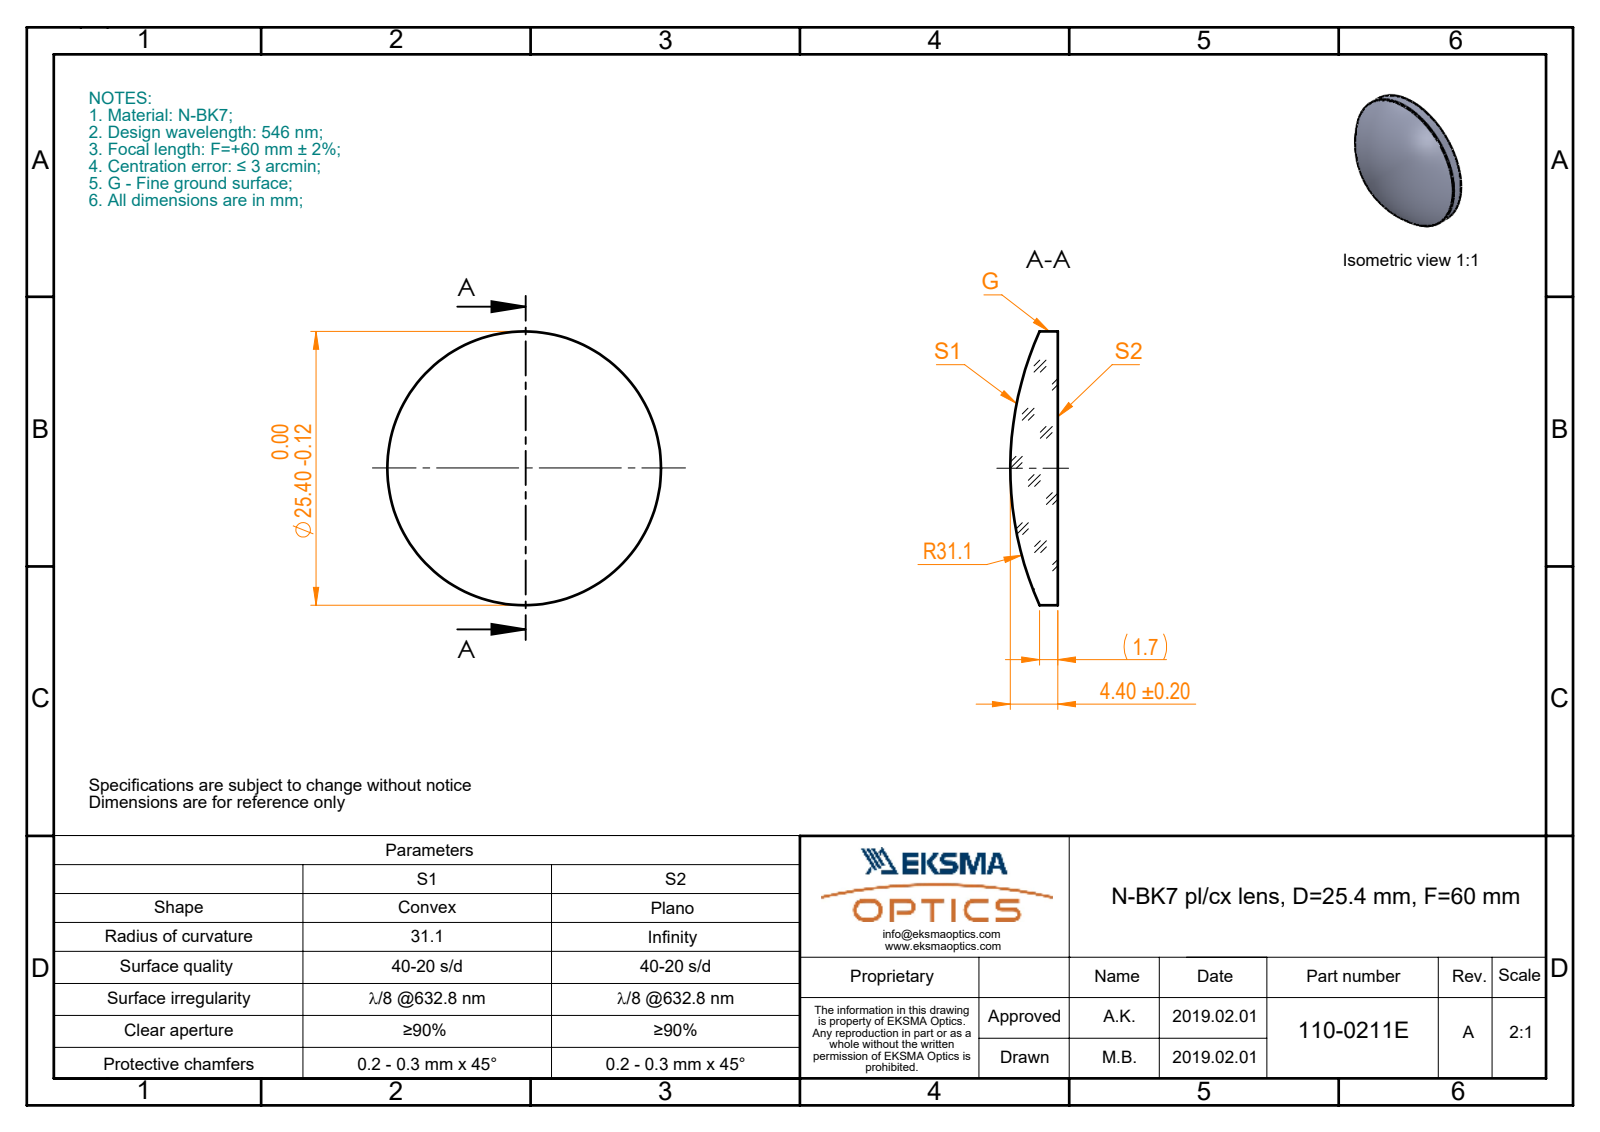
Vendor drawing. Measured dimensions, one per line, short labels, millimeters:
name: 110-0211E BK7 pl-cx 25.4 F60
written by: SolidWorks 2017 (CONFIG_CONTROL_DESIGN)
unit: mm
bodies: 1 solid, 5 faces (1 planar, 2 cylindrical, 2 other)
size: 25.4 × 25.4 × 4.4
volume: 1 554 mm³; area: 1 171 mm²
bosses: 1× ⌀25.4
